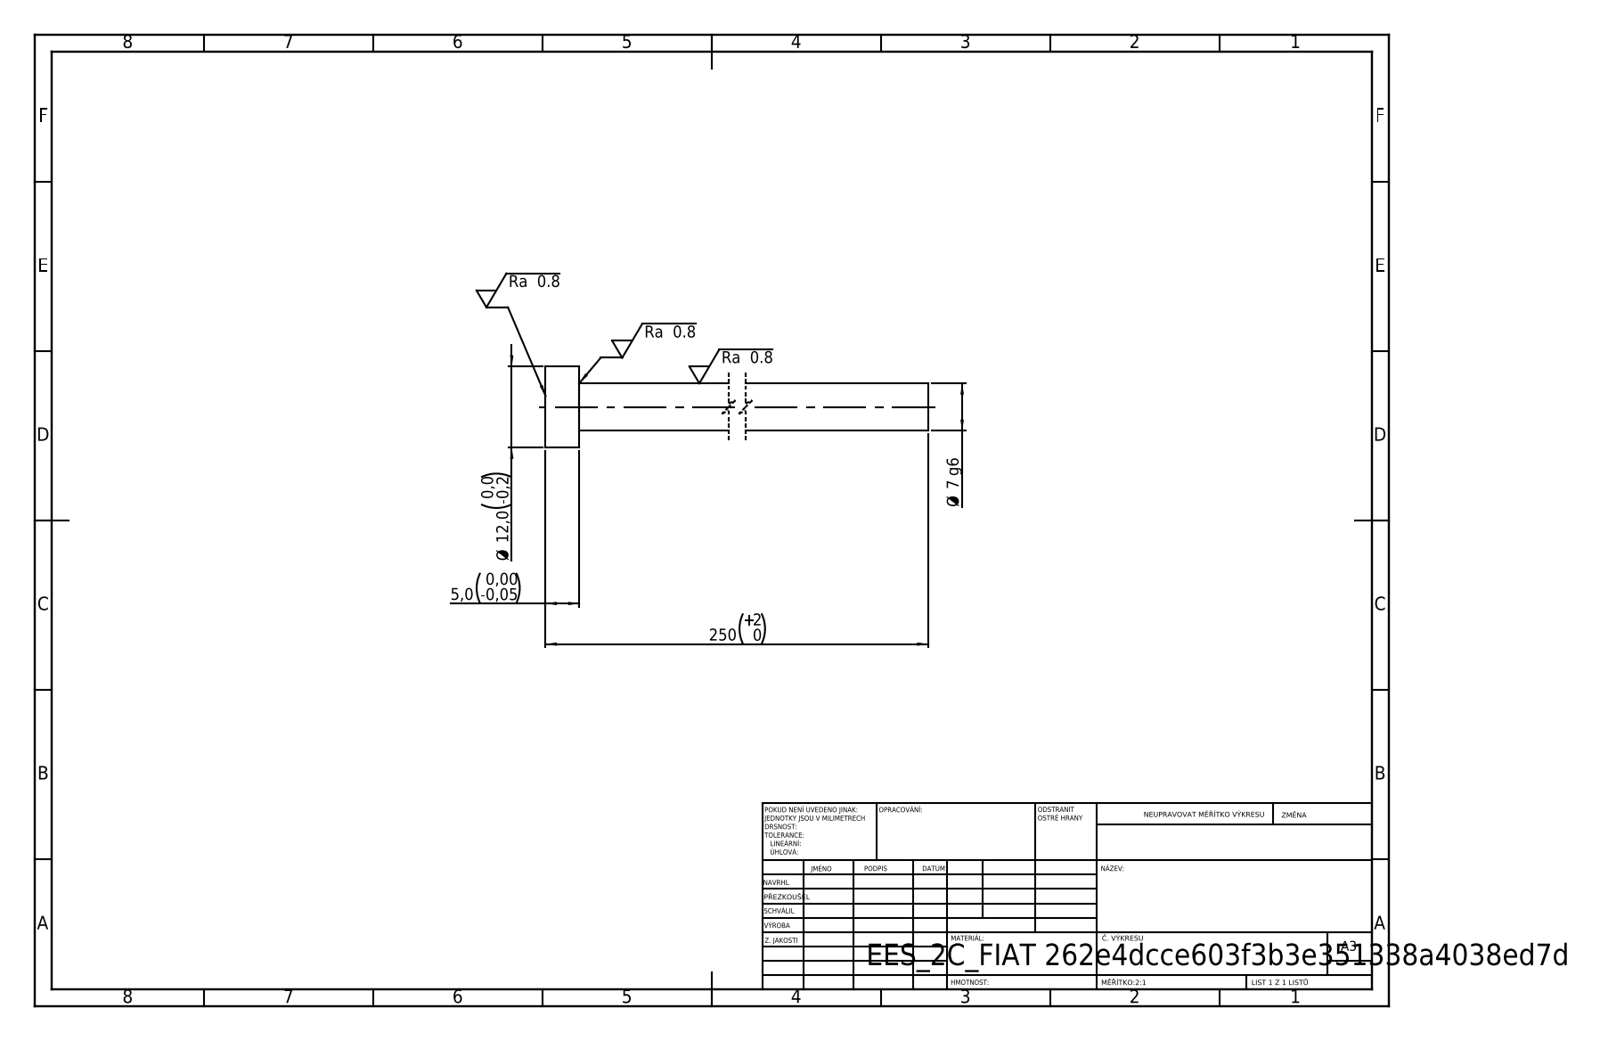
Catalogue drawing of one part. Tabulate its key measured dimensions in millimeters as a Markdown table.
| quantity | value |
| --- | --- |
| STEP written by | SolidWorks 2019 (CONFIG_CONTROL_DESIGN) |
| units | millimeters |
| bodies | 1 solid, 7 faces (3 planar, 4 cylindrical, 0 other) |
| overall size | 250 × 12 × 12 |
| volume | 9 994 mm³ |
| surface area | 5 803 mm² |
| round bosses / shafts (diameter × count) | 12 × 1, 7 × 1 |
| main face-to-face distances | 5, 250, 245 |
